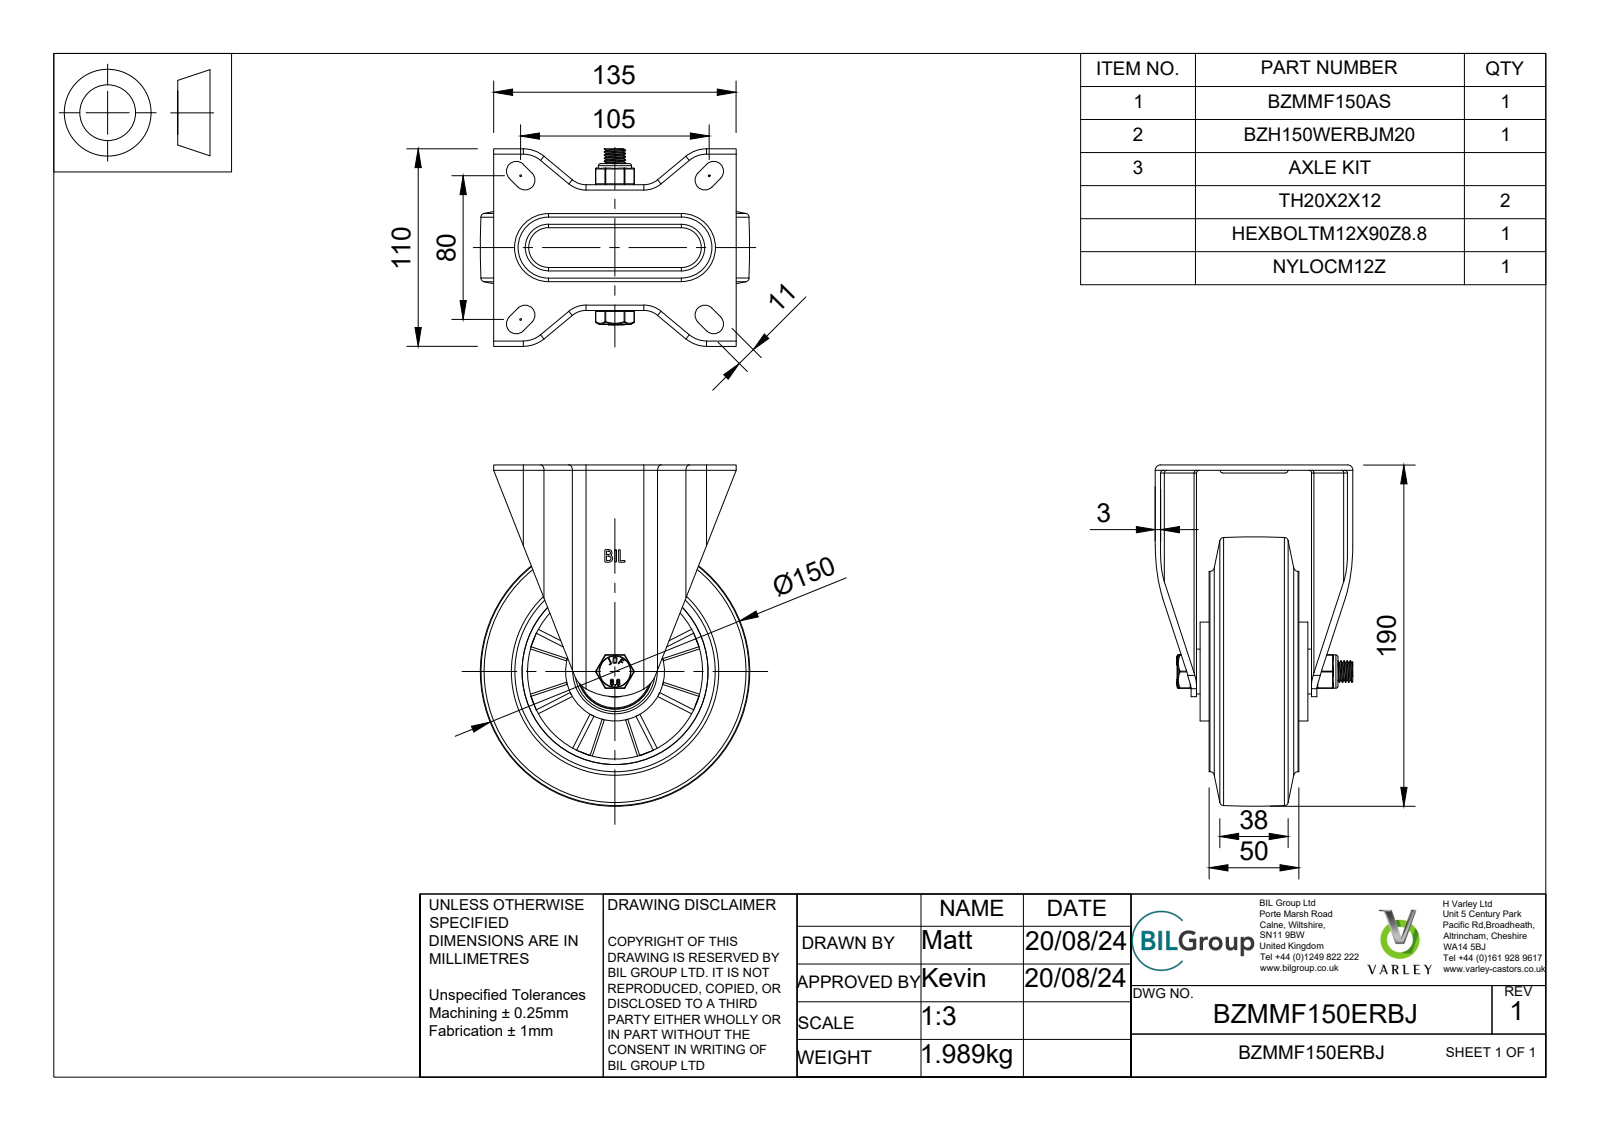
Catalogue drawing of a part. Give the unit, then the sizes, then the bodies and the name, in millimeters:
Units: millimetres
Overall size (bounding box): 190 × 150 × 110
Round holes (diameter × count): ⌀12 ×1, ⌀12.2 ×1, ⌀12.25 ×1, ⌀14 ×1, ⌀20 ×1, ⌀28.5 ×1, ⌀32 ×1, ⌀41.5 ×1, ⌀42 ×1, ⌀44 ×1, ⌀47 ×1, ⌀97.5 ×1
Round bosses / shafts (diameter × count): ⌀111.5 ×1, ⌀55 ×1, ⌀40.5 ×1, ⌀40 ×1, ⌀29 ×1, ⌀27 ×1, ⌀25 ×1, ⌀19.8 ×1
Partial cylindrical surfaces — rounded edges, fillets, slot ends (radius × count): R0.5 ×20, R6 ×16, R1.5 ×12, R4 ×12, R3 ×8, R5.5 ×8, R0.47 ×4, R0.9 ×4
Main face-to-face distances: 3, 67, 24.74, 16, 51, 60, 35.5, 5, 64, 7
Volume: 688 465 mm³ · Surface area: 250 841 mm²
Bodies: 35 solids, 1516 faces (669 planar, 305 cylindrical, 542 other)
Part name (STEP PRODUCT): BZMMF150ERBJ v3; BZMMF150AS - 64 v1; ZINC PLATED, PRESSED STEEL BRACKET; BZH150WERBJM20 v1 (+8 more)
STEP written by: Autodesk Translation Framework v13.14.0.145 (AUTOMOTIVE_DESIGN)
